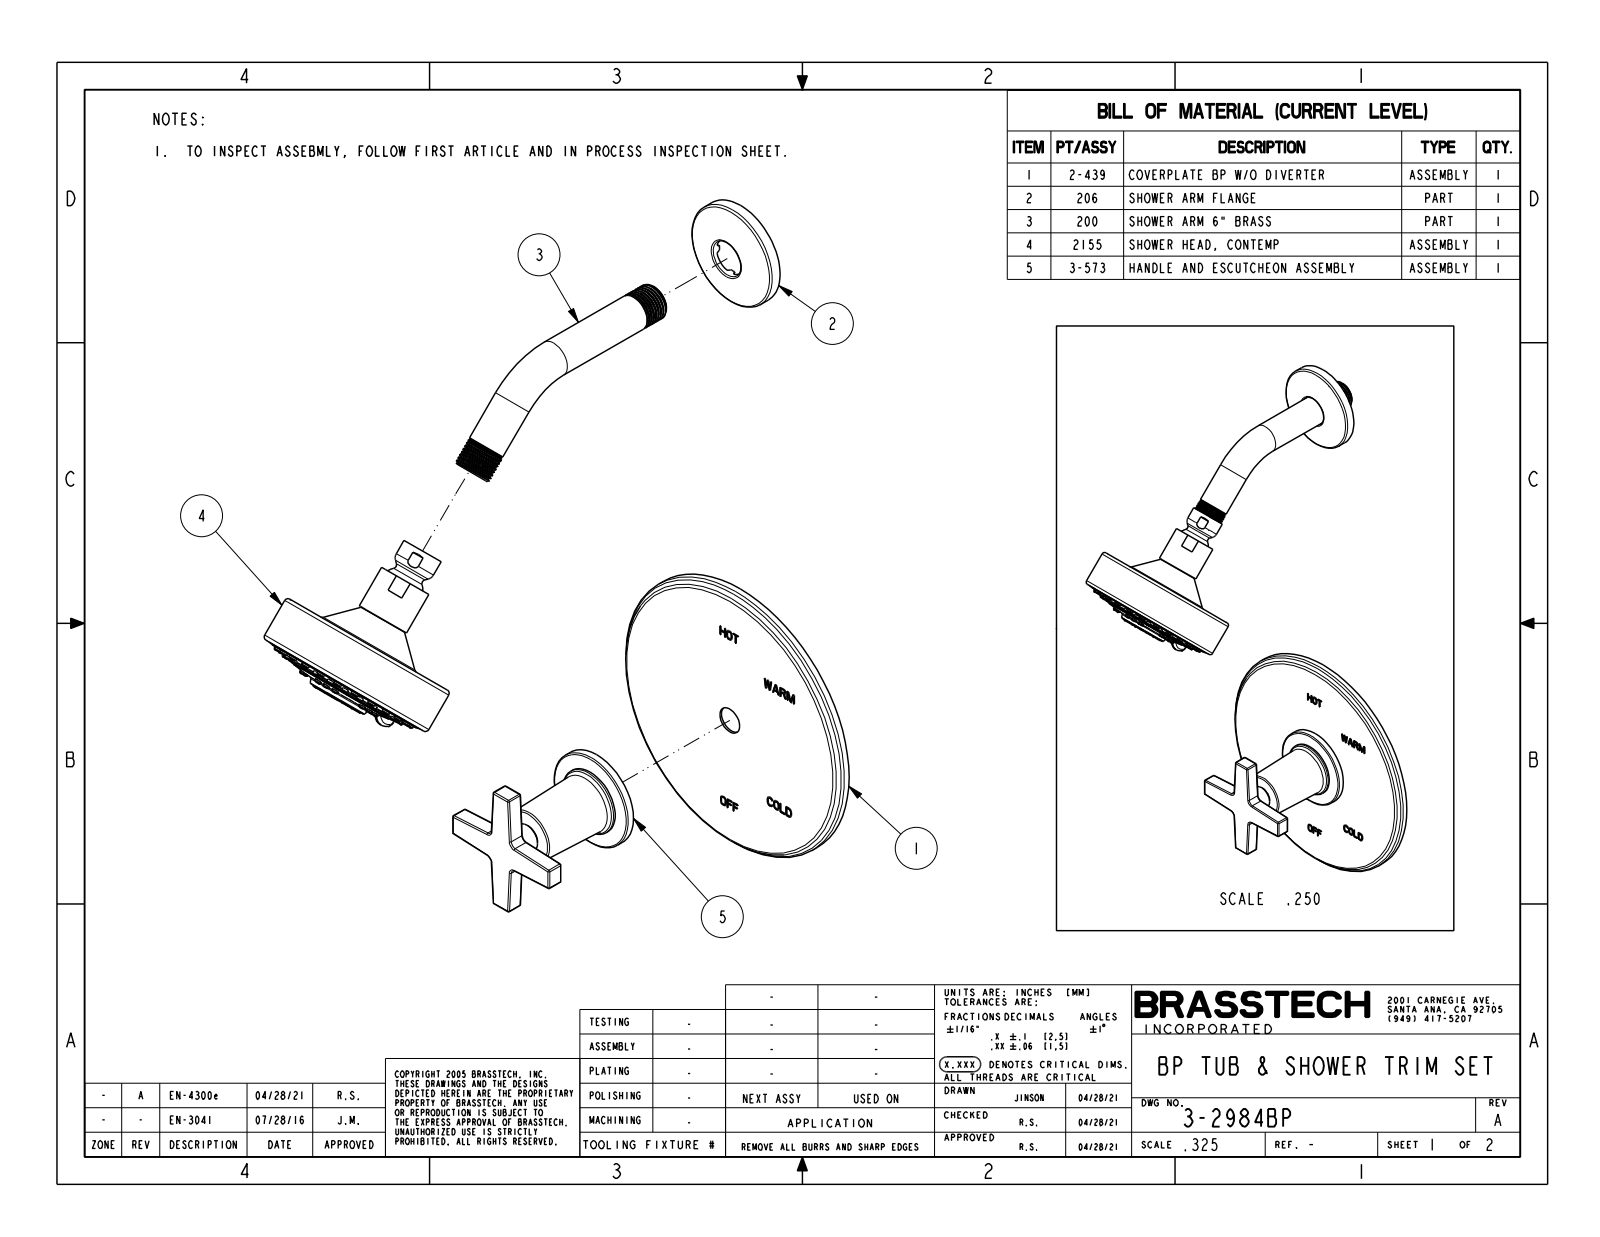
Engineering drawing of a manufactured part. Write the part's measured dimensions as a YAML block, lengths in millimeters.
part_name: "3-2984BP"
step_written_by: "CREO PARAMETRIC BY PTC INC, 2018400 (CONFIG_CONTROL_DESIGN)"
units: millimeters
bodies: {solids: 2, faces: 1479, planar: 478, cylindrical: 238, other: 763}
overall_size: [417.6, 207.6, 165.1]
volume: 573900
surface_area: 105700
round_holes:
  - {diameter: 1.5, count: 8}
  - {diameter: 23.5, count: 1}
round_bosses_or_shafts:
  - {diameter: 3.6, count: 39}
  - {diameter: 4.2, count: 23}
  - {diameter: 20.7, count: 2}
  - {diameter: 165.1, count: 1}
  - {diameter: 101.6, count: 1}
  - {diameter: 94.6, count: 1}
  - {diameter: 60.5, count: 1}
  - {diameter: 59, count: 1}
partial_cylinders:
  - {radius: 0.8, count: 32}
  - {radius: 2, count: 8}
  - {radius: 3.2, count: 4}
  - {radius: 0.5, count: 2}
  - {radius: 3.5, count: 1}
  - {radius: 12, count: 1}
  - {radius: 13, count: 1}
  - {radius: 16, count: 1}
face_to_face_distances: [8, 80.8, 72.9, 4.7, 12.7, 68.1, 71.3, 63.4, 58.6, 9.5]
hole_center_spacings: [11.3, 14.7, 20.8, 20.8, 27.2, 11.3, 14.7, 27.2]
